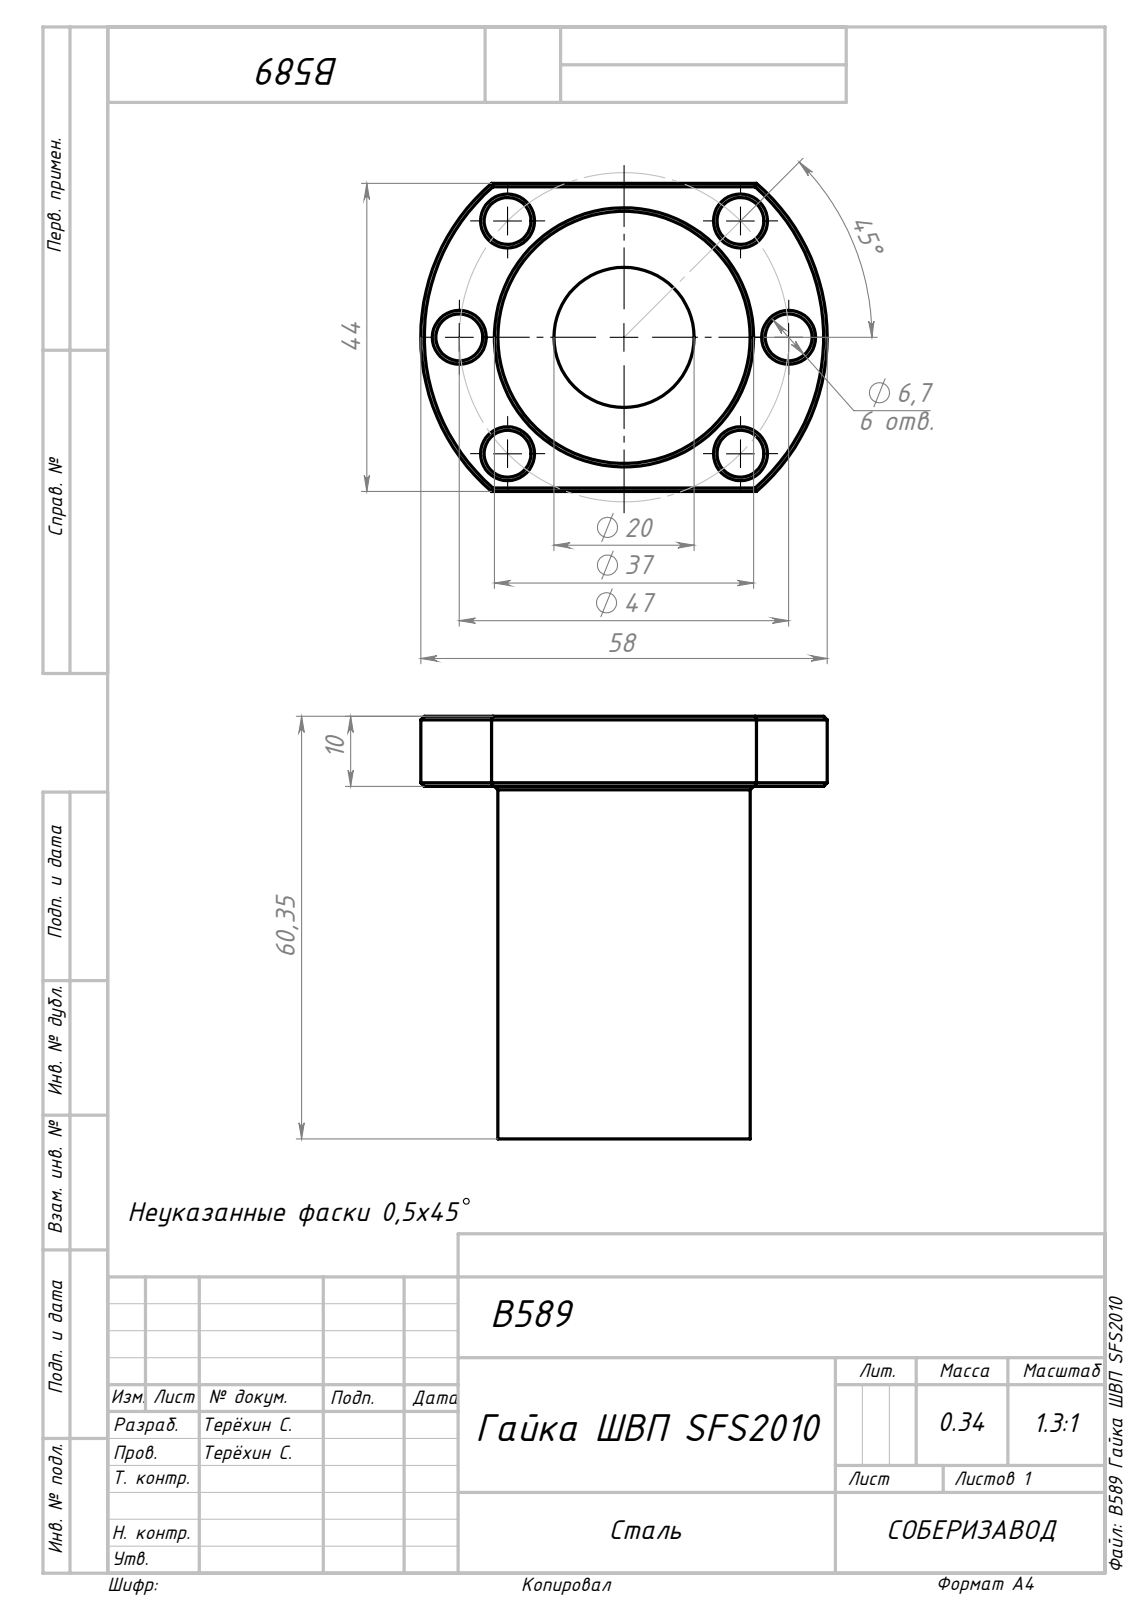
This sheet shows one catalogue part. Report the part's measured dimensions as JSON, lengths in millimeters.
{"part_name": "B589 Гайка ШВП SFS2010_00; Сборка1", "step_written_by": "SolidWorks 2024 (AUTOMOTIVE_DESIGN)", "units": "millimeters", "bodies": {"solids": 1, "faces": 62, "planar": 9, "cylindrical": 19, "other": 34}, "overall_size": [60.35, 58, 44], "volume_mm3": 52904, "surface_area_mm2": 15788, "round_holes": [[6.7, 6], [20, 1]], "round_bosses_or_shafts": [[36, 1]], "partial_cylinders_radius": [[29, 1]], "face_to_face_distances": [10, 60.35, 50.35, 44, 37.47], "hole_center_spacings": [23.5, 17.99, 33.24, 43.43, 47.01, 47]}
